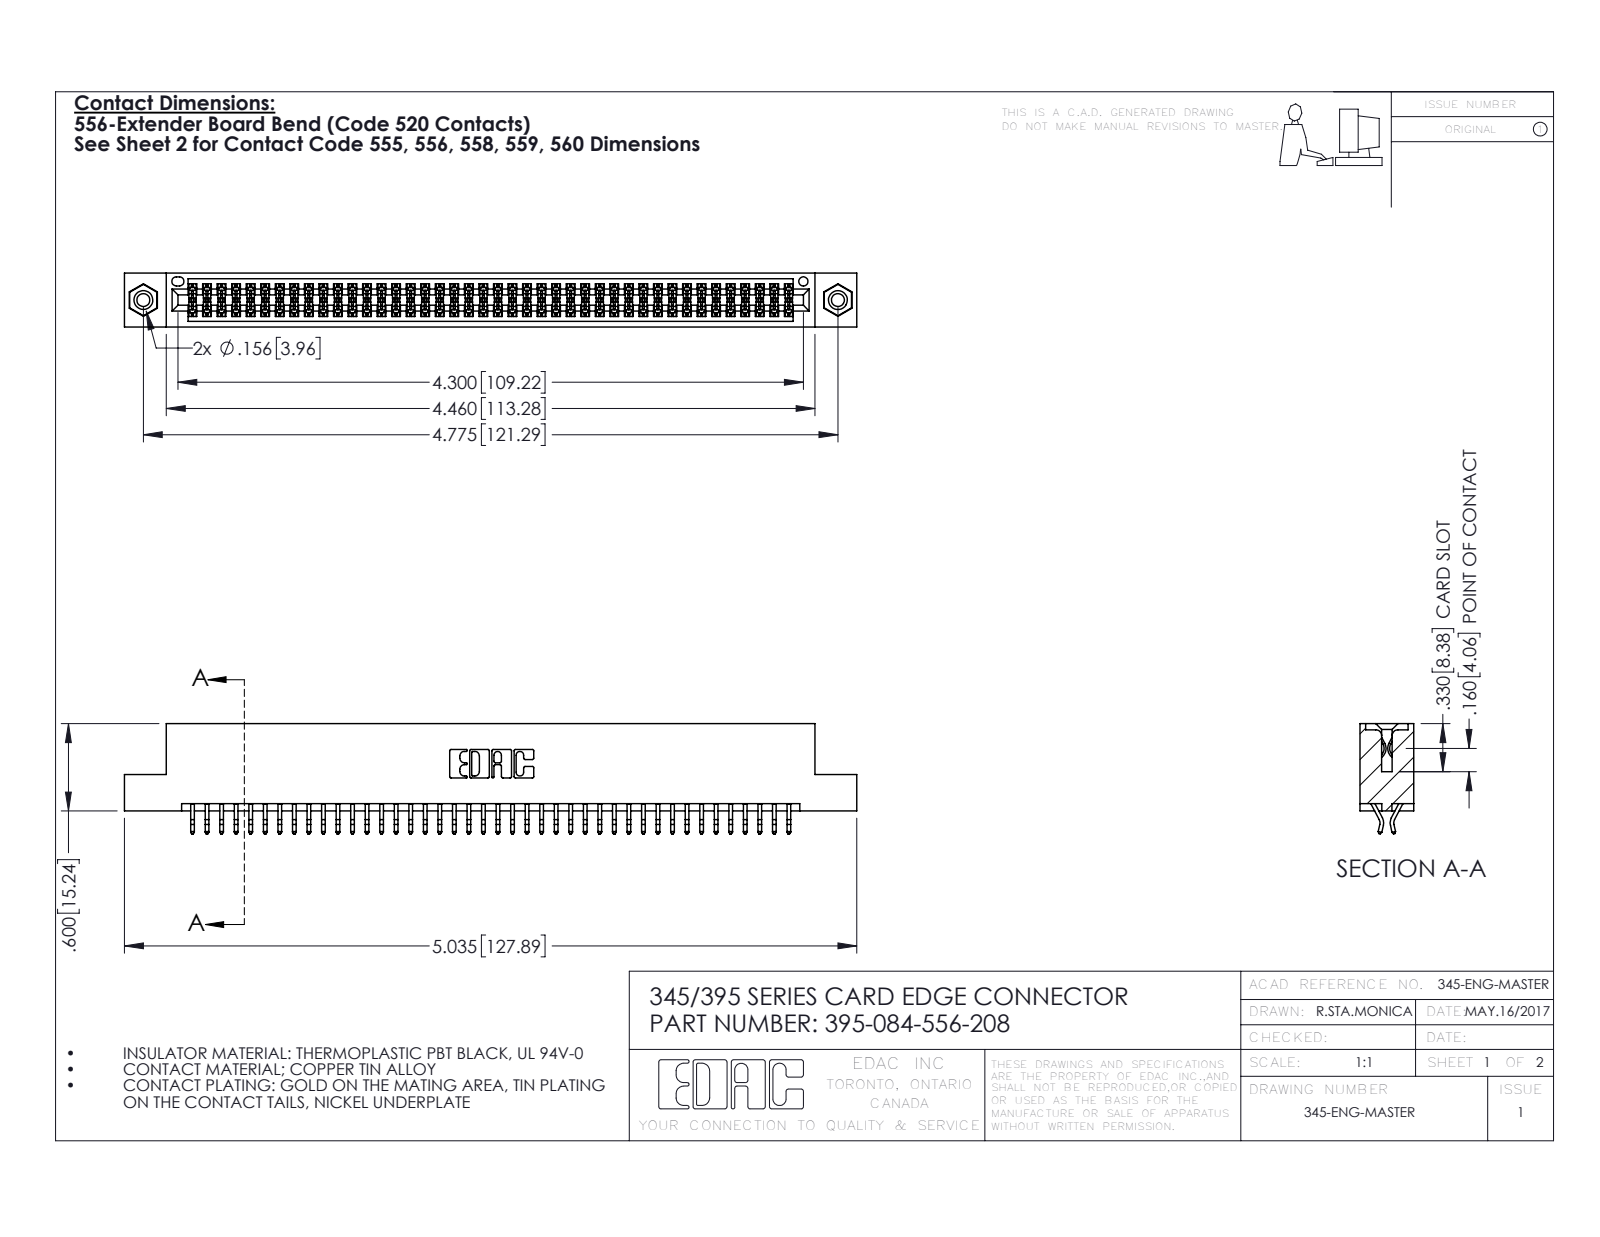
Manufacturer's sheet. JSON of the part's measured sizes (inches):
{"part_name": "345 Part_Flush Mounting Lugs - 0.156 Dia-TI; 395-084-556-208; 345-250-001_345-250-003-102; 345-292-001_556 Tail", "step_written_by": "SolidWorks 2016 (CONFIG_CONTROL_DESIGN)", "units": "inches", "bodies": {"solids": 87, "faces": 4890, "planar": 3220, "cylindrical": 1654, "other": 16}, "overall_size": [5.035, 0.757, 0.37], "volume_in3": 0.758, "surface_area_in2": 28.35, "round_holes": [[0.089, 2], [0.125, 2], [0.156, 2], [0.064, 1]], "round_bosses_or_shafts": [[0.155, 2]], "partial_cylinders_radius": [[0.006, 126], [0.01, 22], [0.007, 6], [0.031, 6], [0.026, 3], [0.01, 2], [0.014, 2], [0.019, 2]], "face_to_face_distances": [0.072, 0.298, 0.2, 0.37, 0.025, 0.098, 0.272, 0.225, 0.175, 0.149], "hole_center_spacings": [0.27, 4.539, 4.775]}
